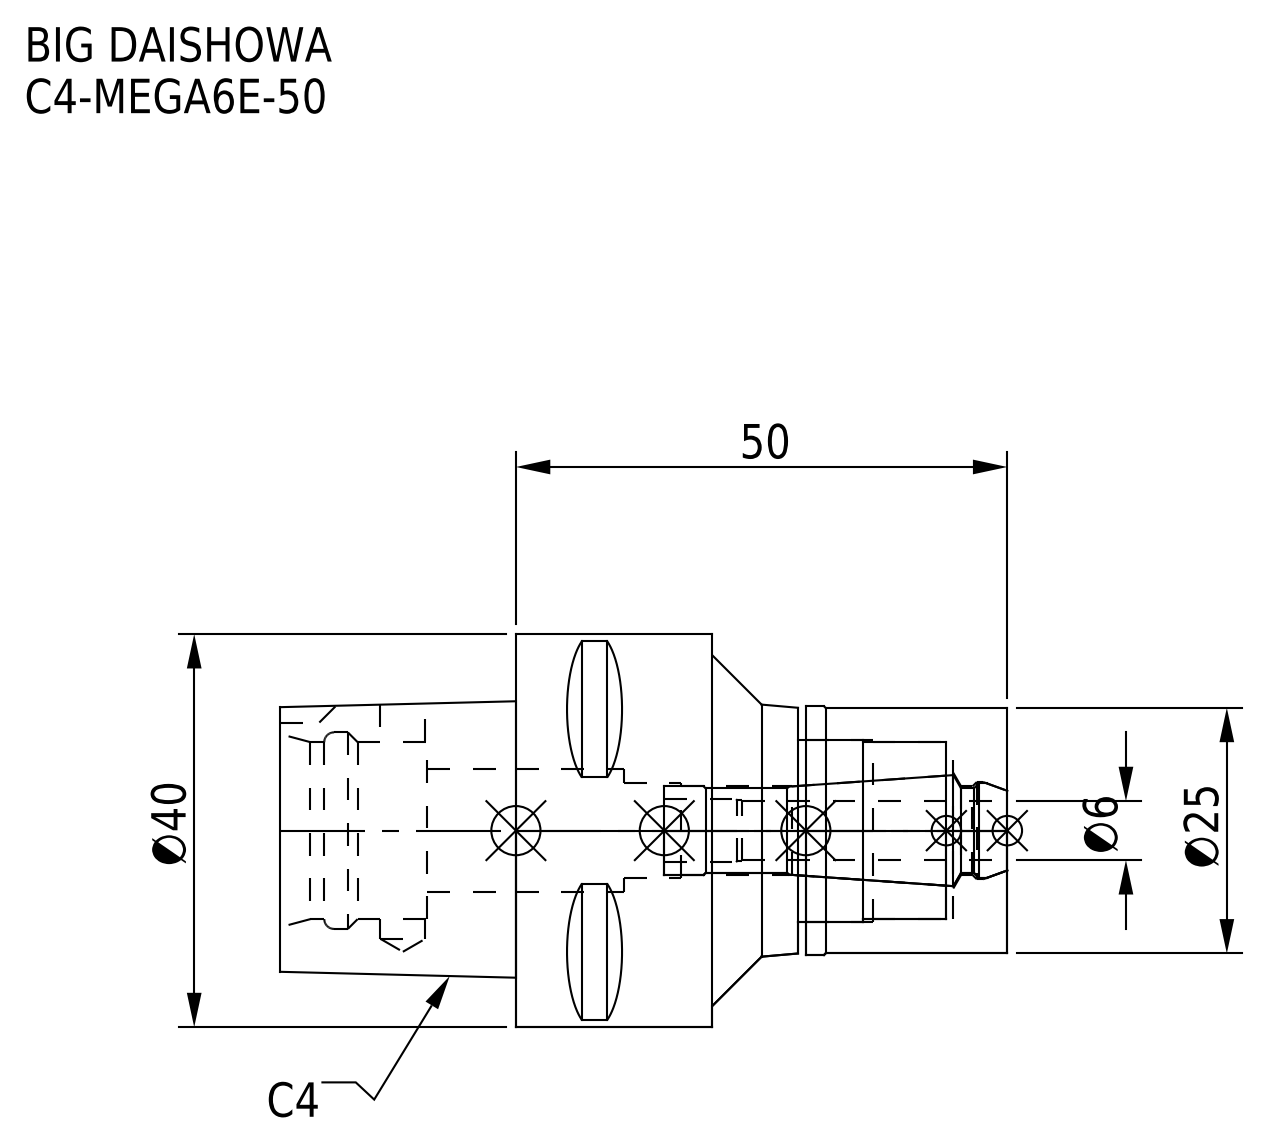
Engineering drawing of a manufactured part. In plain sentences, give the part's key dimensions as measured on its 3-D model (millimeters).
The part is named "C4-MEGA6E-50; DXF_TEMP_ASSY_ASM_4_ASM.stp; C4-MEGA6E-50_1.stp; MEN6_1.stp (+3 more)". Its 3-D file was written by "SolidWorks 2019 (CONFIG_CONTROL_DESIGN)". It is 2 solids with 94 faces: 35 planar, 35 cylindrical and 24 other. Overall it measures 74 by 40 by 40 millimeters. Its volume is 45 022 cubic millimeters and its surface area 14 573 square millimeters. Round holes: 1 of diameter 4.6, 1 of diameter 9, 1 of diameter 9.6, 1 of diameter 9.9, 1 of diameter 12.5, 1 of diameter 18, 1 of diameter 18.5, 1 of diameter 20. Round bosses or shafts: 1 of diameter 40, 1 of diameter 25.3, 1 of diameter 25. Partial cylindrical surfaces (rounded edges, fillets, slot ends): 1 of radius 3. The main face-to-face distances are 50, 53.5, 20, 15, 30, 20.5, 9.5, 29.5, 21.3, 0.8.
